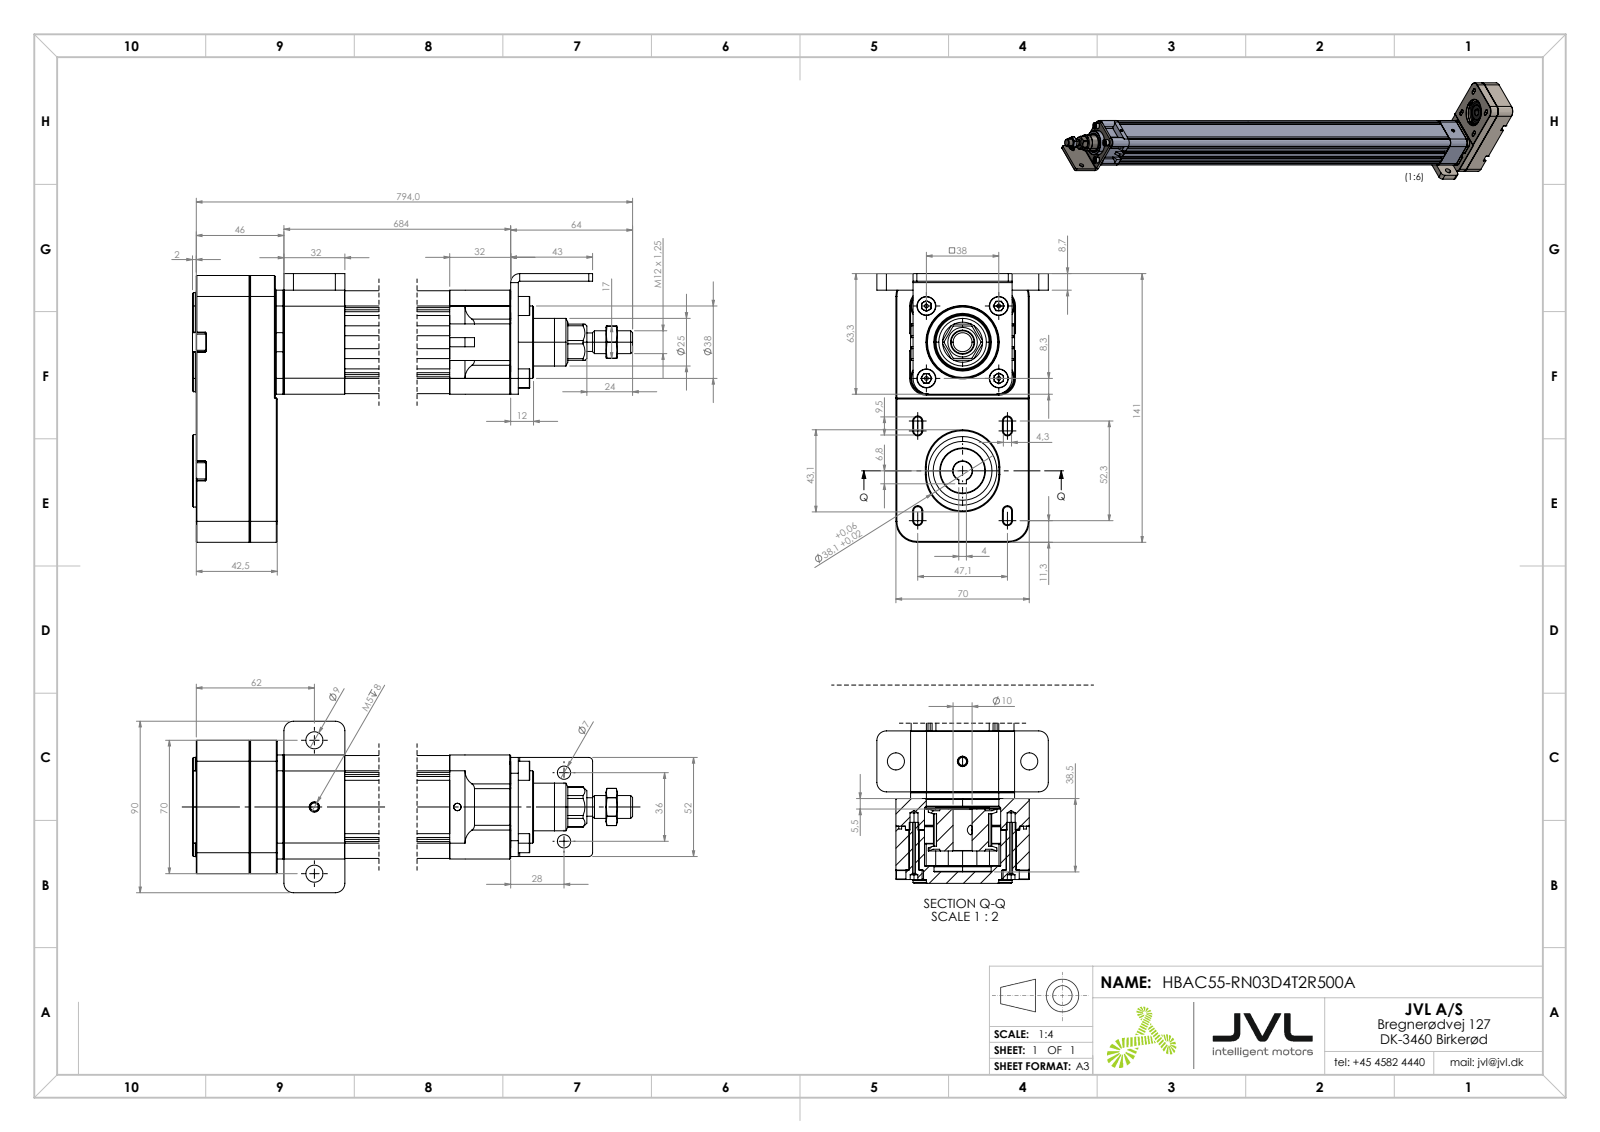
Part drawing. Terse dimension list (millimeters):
name: HBAC55-RN03D4T2R500A (standalone); HBAC55-LB; HBAC55-DZ; HBAC55-RN03D4T2R500A (assembly)
written by: SolidWorks 2023 (AUTOMOTIVE_DESIGN)
unit: mm
bodies: 2 solids, 3149 faces (1110 planar, 1167 cylindrical, 872 other)
size: 796 × 141 × 90
volume: 37 995 mm³; area: 637 044 mm²
holes: 11× ⌀1.5, 9× ⌀5, 6× ⌀3.3, 6× ⌀4.2, 6× ⌀4.3, 5× ⌀5.3, 4× ⌀2, 4× ⌀5.2, 4× ⌀6, 4× ⌀6.4, 4× ⌀6.5, 4× ⌀9.5
bosses: 8× ⌀10, 6× ⌀7, 6× ⌀4, 5× ⌀8.5, 5× ⌀5, 4× ⌀9, 4× ⌀6, 3× ⌀3
rounds: 84× R0.25, 82× R0.55, 82× R3.27, 33× R0.5, 10× R4, 8× R0.3, 8× R2.15, 8× R3
face distances: 54, 4.5, 31, 8, 5, 49.5, 4, 62, 12, 50
hole spacings: 31.27, 10.88, 12.24, 15.99, 18.15, 19.24, 20.08, 22.62
